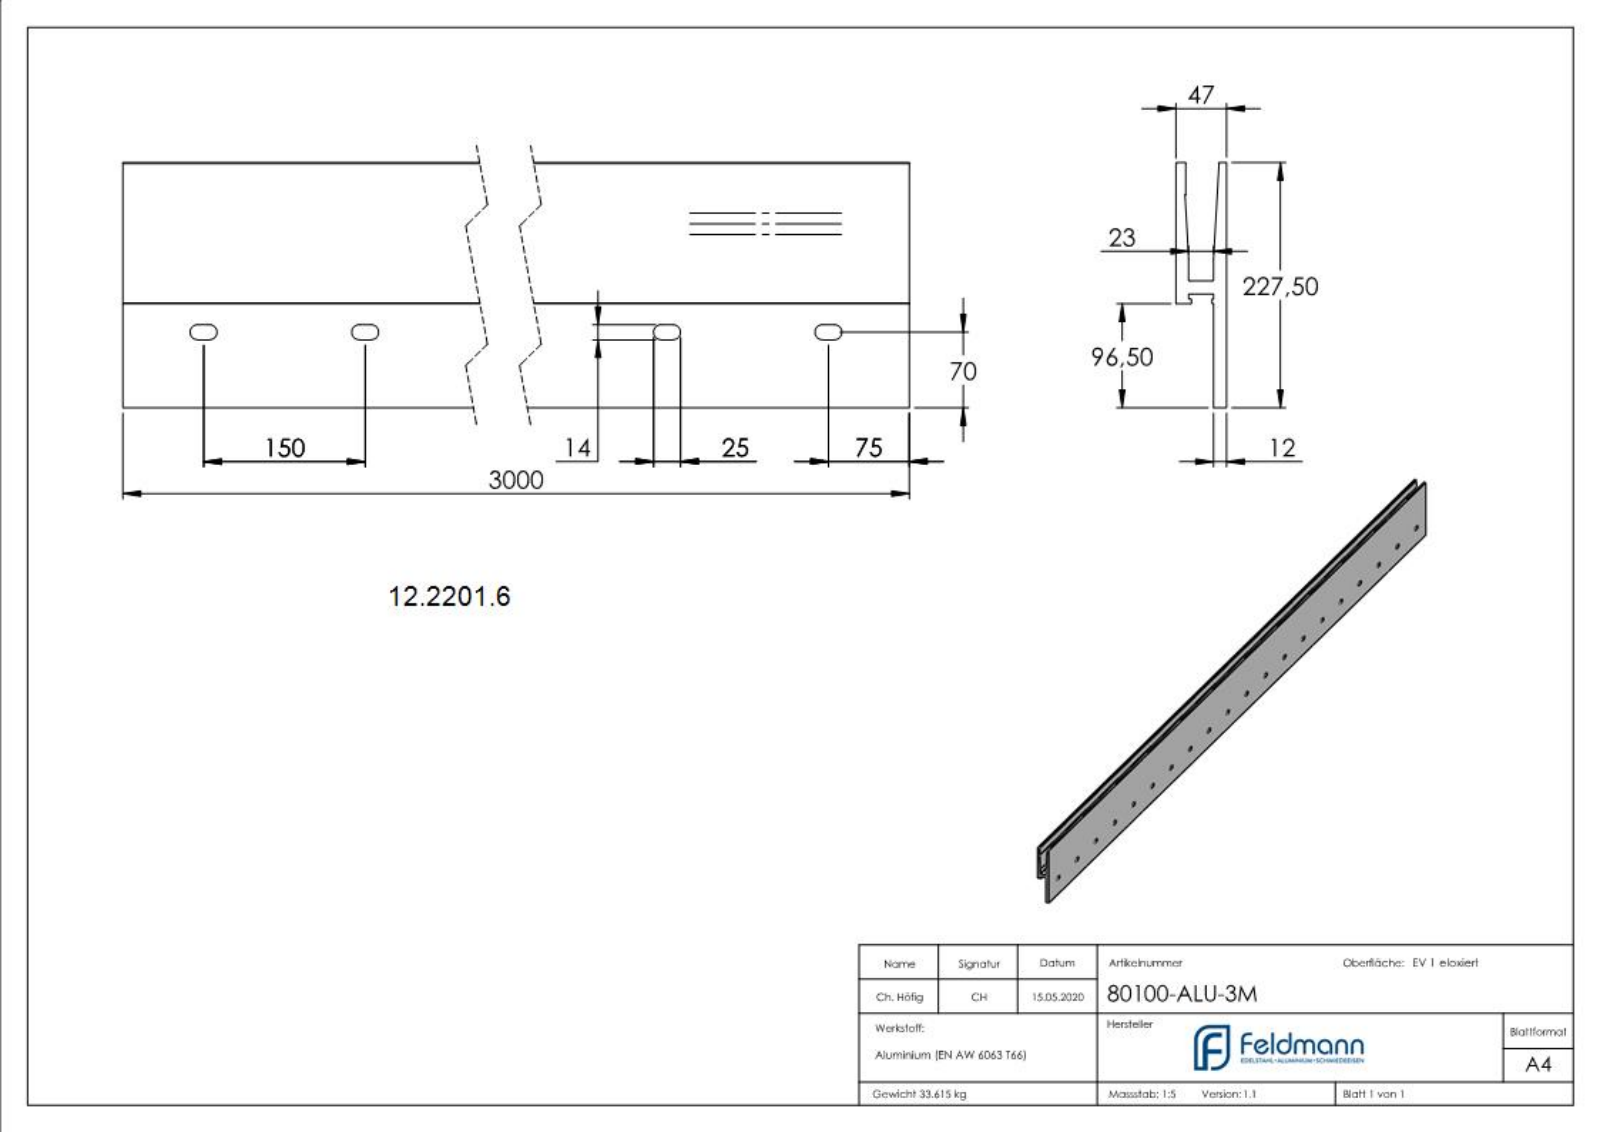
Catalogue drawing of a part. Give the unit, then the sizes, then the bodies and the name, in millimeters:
Units: millimetres
Overall size (bounding box): 3000 × 227.5 × 47
Partial cylindrical surfaces — rounded edges, fillets, slot ends (radius × count): R7 ×40, R0.5 ×9, R1 ×3, R0.65 ×2, R0.25 ×1
Main face-to-face distances: 12, 35, 47, 37.8, 9.2, 25.8, 2.8, 23, 122, 110
Volume: 12 450 000 mm³ · Surface area: 2 365 000 mm²
Bodies: 1 solid, 369 faces (200 planar, 56 cylindrical, 113 other)
Part name (STEP PRODUCT): 80100-ALU-3M
STEP written by: SolidWorks 2015 (CONFIG_CONTROL_DESIGN)
